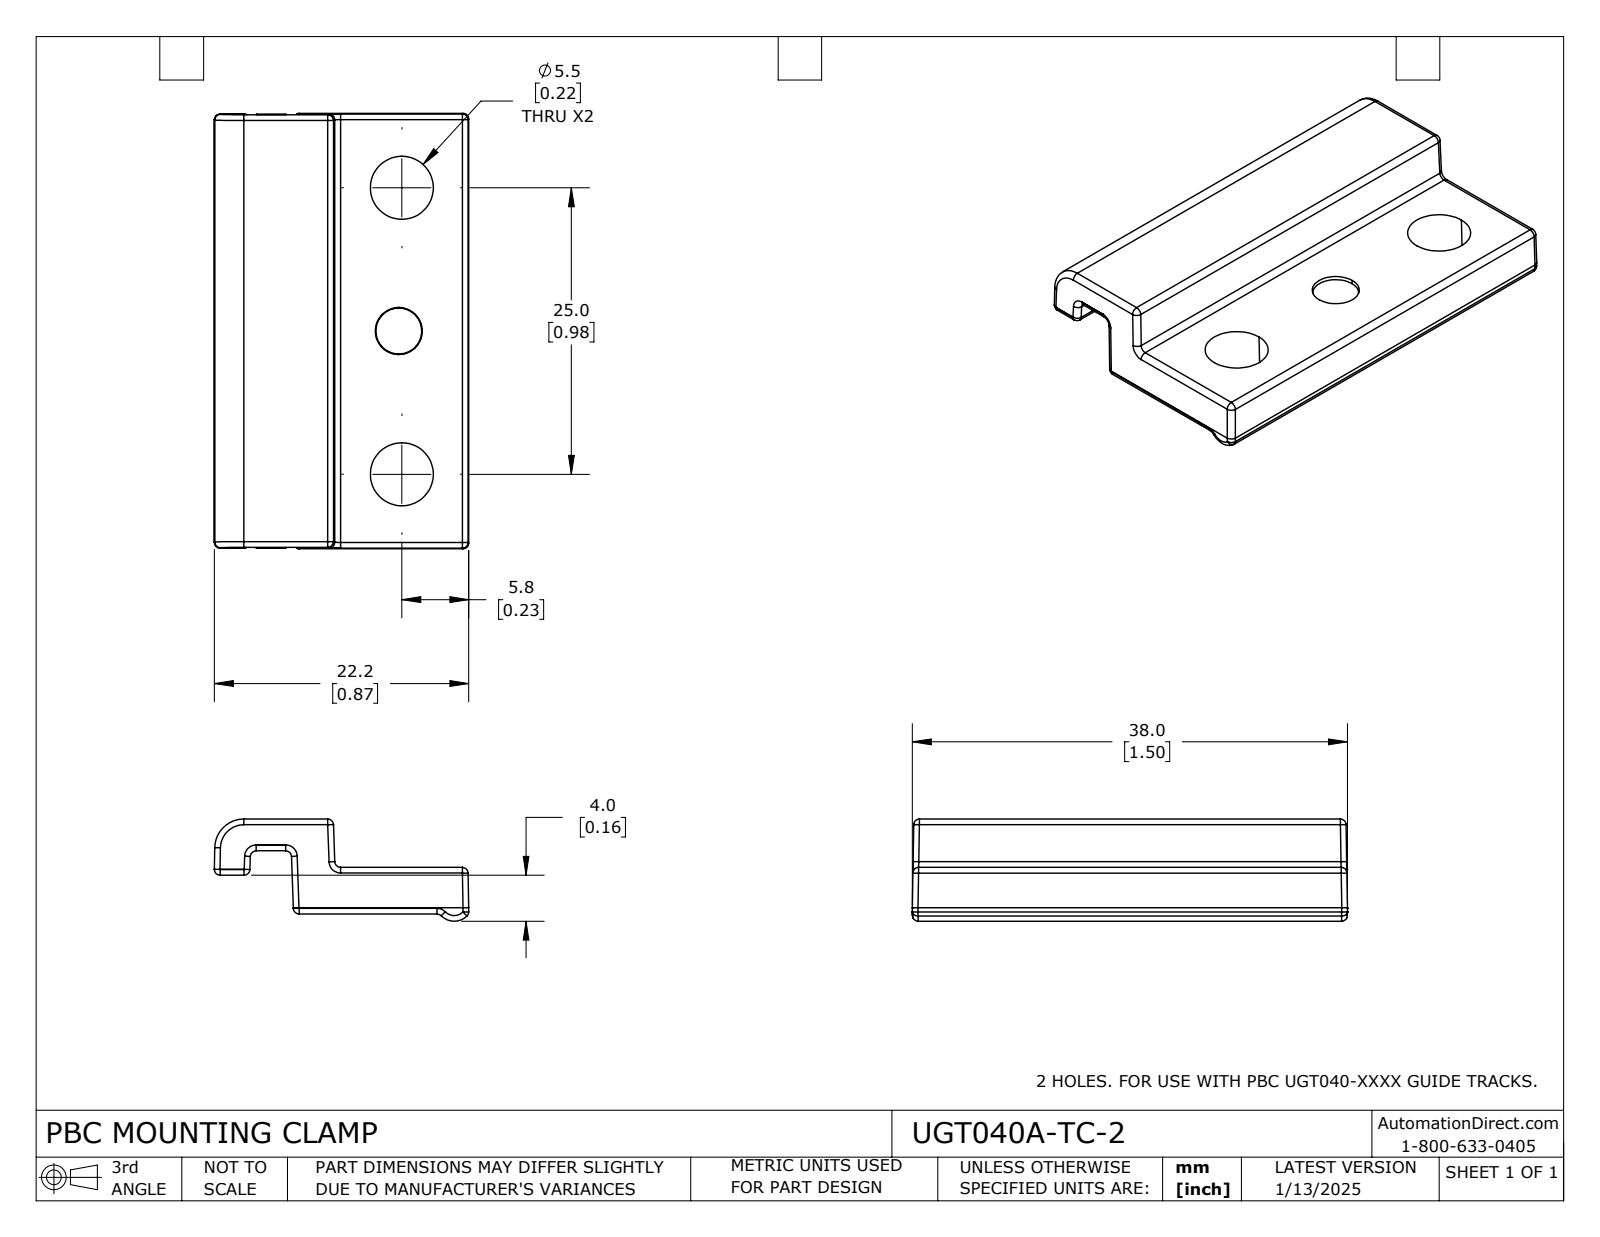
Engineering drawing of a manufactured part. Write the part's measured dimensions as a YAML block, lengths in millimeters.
part_name: "UGT040A-TC-2"
step_written_by: "SolidWorks 2023 (CONFIG_CONTROL_DESIGN)"
units: millimeters
bodies: {solids: 1, faces: 87, planar: 16, cylindrical: 41, other: 30}
overall_size: [38, 22.2, 8.9]
volume: 3690
surface_area: 2590
partial_cylinders:
  - {radius: 0.5, count: 24}
  - {radius: 0.5, count: 10}
  - {radius: 1.6, count: 1}
  - {radius: 2.5, count: 1}
face_to_face_distances: [4.1, 8.3, 4.2, 3.8, 5.5, 1.4, 2.8, 3.4, 0.7, 2.1]
